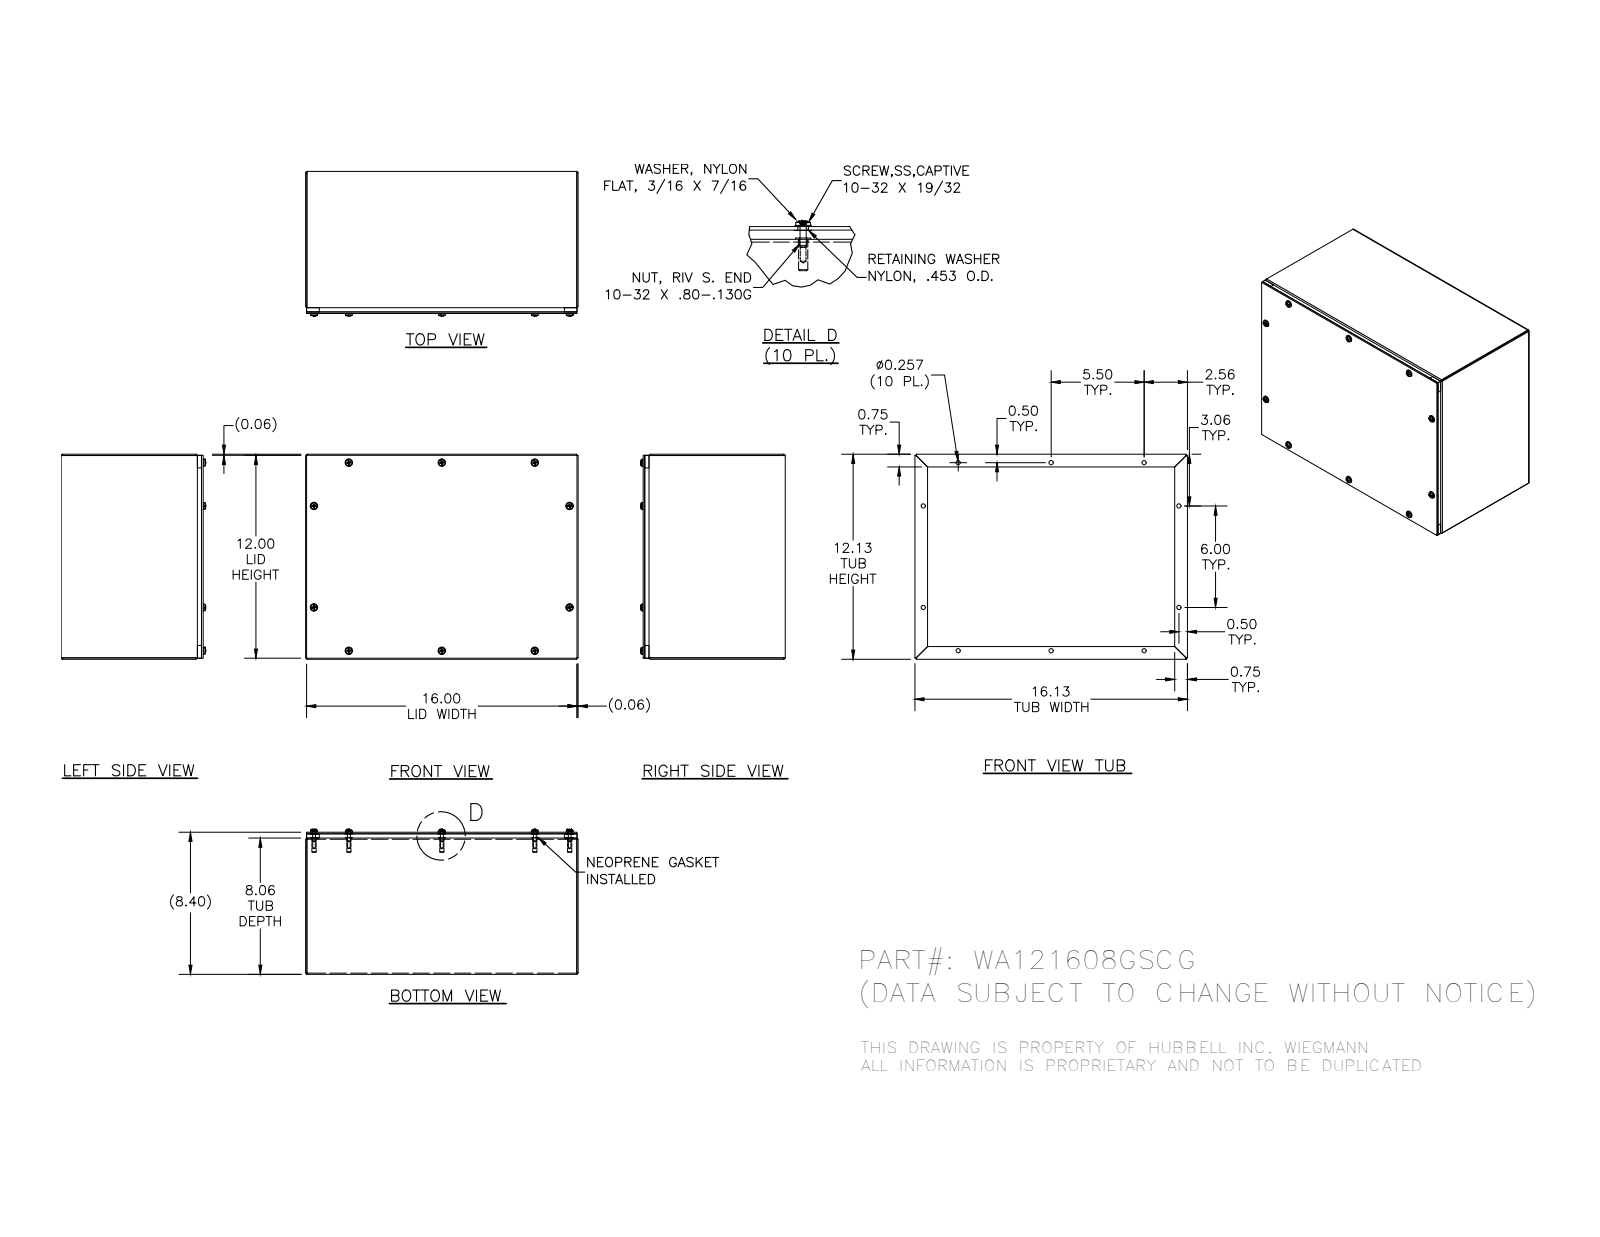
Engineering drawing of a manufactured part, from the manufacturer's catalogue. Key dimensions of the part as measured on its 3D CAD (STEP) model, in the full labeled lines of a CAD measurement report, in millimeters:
Part name (STEP PRODUCT): 39035; 37210; WA121608GSCGBKP; 34984 (+3 more)
STEP written by: SolidWorks 2014 (AUTOMOTIVE_DESIGN)
Units: millimetres
Bodies: 46 solids, 1070 faces (508 planar, 276 cylindrical, 286 other)
Overall size (bounding box): 409.6 × 308 × 217.4
Volume: 1 294 000 mm³ · Surface area: 1 217 000 mm²
Round holes (diameter × count): ⌀4 ×10, ⌀4.8 ×10, ⌀5 ×10, ⌀6.5 ×10, ⌀7.1 ×10, ⌀7.1 ×10
Round bosses / shafts (diameter × count): ⌀11.5 ×10, ⌀11.1 ×10, ⌀10.3 ×10, ⌀6.3 ×10, ⌀4.2 ×10
Partial cylindrical surfaces — rounded edges, fillets, slot ends (radius × count): R2.3 ×10, R0.4 ×8, R2.3 ×8
Main face-to-face distances: 1.9, 1.9, 2.4, 211.6, 209.2, 213.5, 211.1, 306.1, 308, 304.2
Hole centre spacings: 139.7, 279.4, 202.8, 223.7, 338.1, 338.1, 83.5, 83.5
